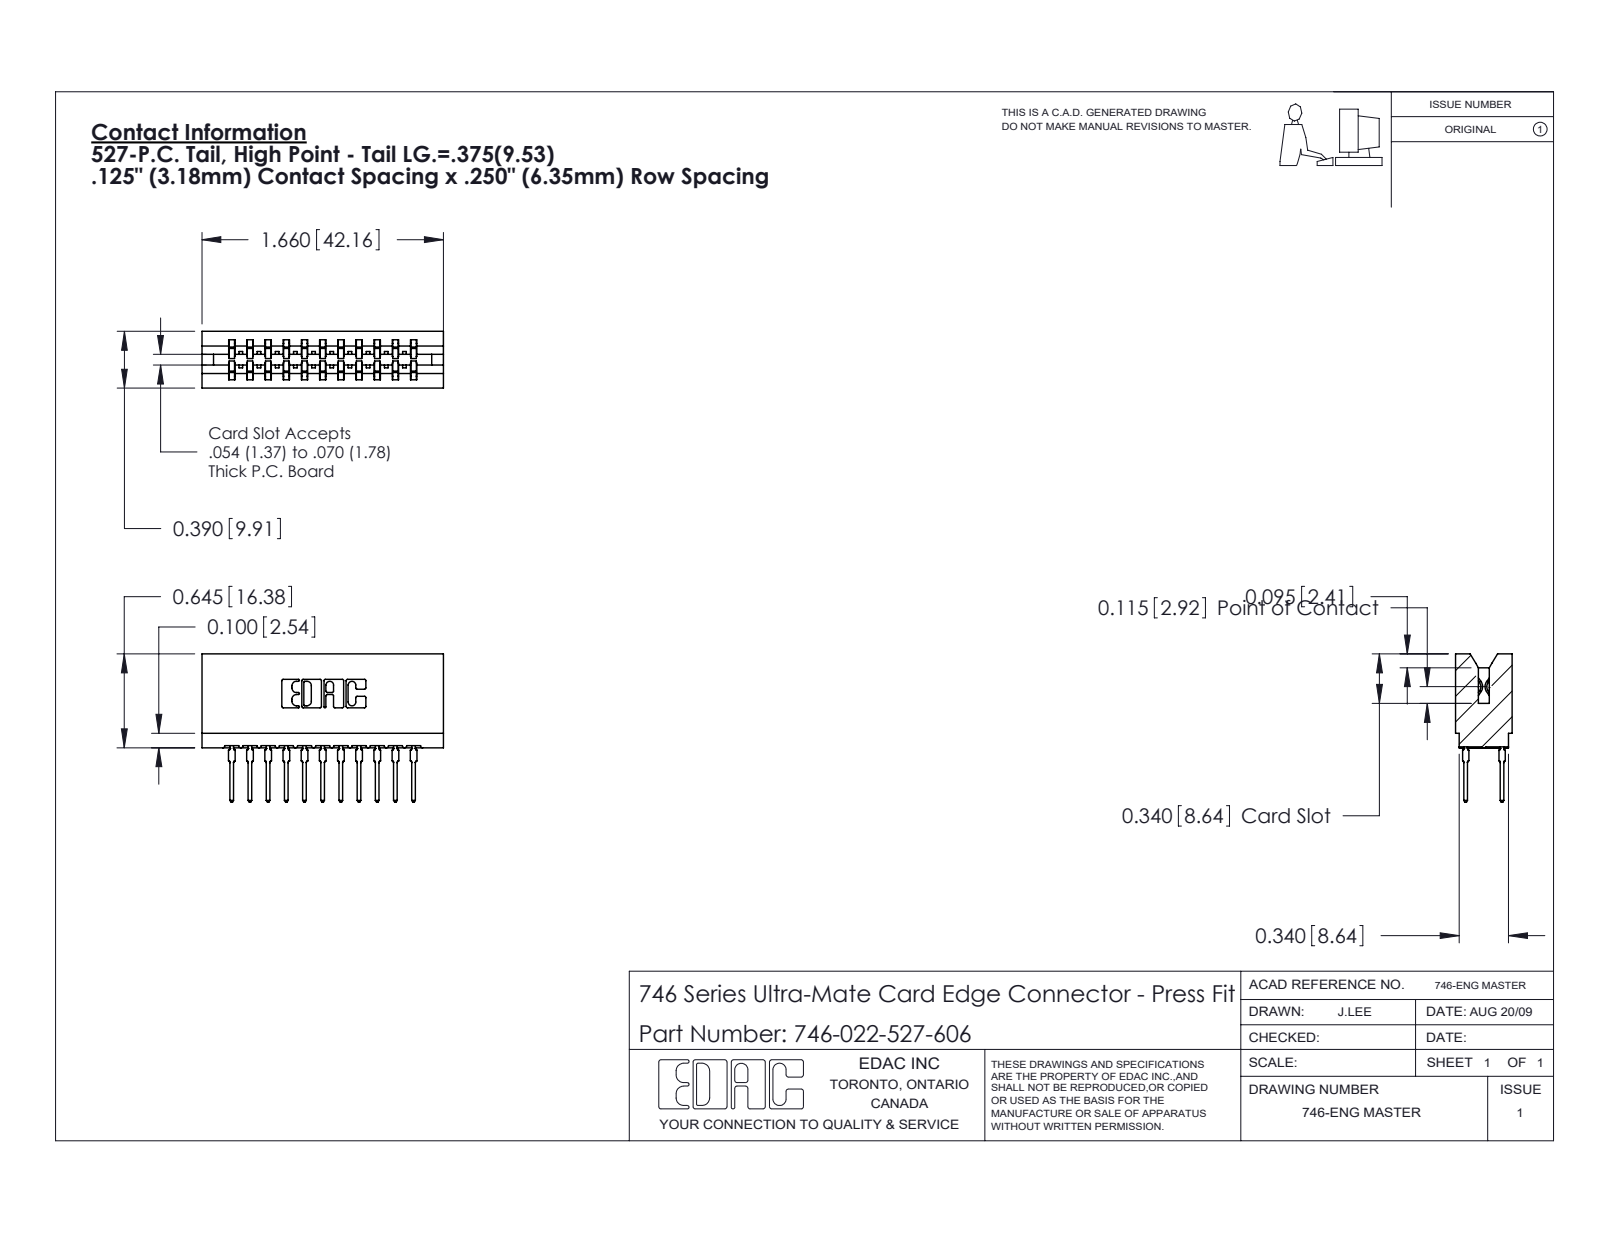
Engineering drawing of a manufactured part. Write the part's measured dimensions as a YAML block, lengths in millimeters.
part_name: "746 Part_.340 Slot Depth - 06; 746-022-527-606; 746-292-001_527"
step_written_by: "SolidWorks 2020 (CONFIG_CONTROL_DESIGN)"
units: millimeters
bodies: {solids: 23, faces: 2067, planar: 1068, cylindrical: 427, other: 572}
overall_size: [42.2, 25.9, 9.9]
volume: 5030
surface_area: 7006
partial_cylinders:
  - {radius: 0.5, count: 44}
  - {radius: 0.3, count: 22}
  - {radius: 0.4, count: 12}
  - {radius: 0.1, count: 8}
  - {radius: 0.3, count: 8}
  - {radius: 0.2, count: 6}
  - {radius: 0.8, count: 6}
  - {radius: 0.7, count: 3}
face_to_face_distances: [6.4, 8.5, 1.4, 12.7, 3.2, 2.1, 1.1, 3.2, 7.4, 13.8]
